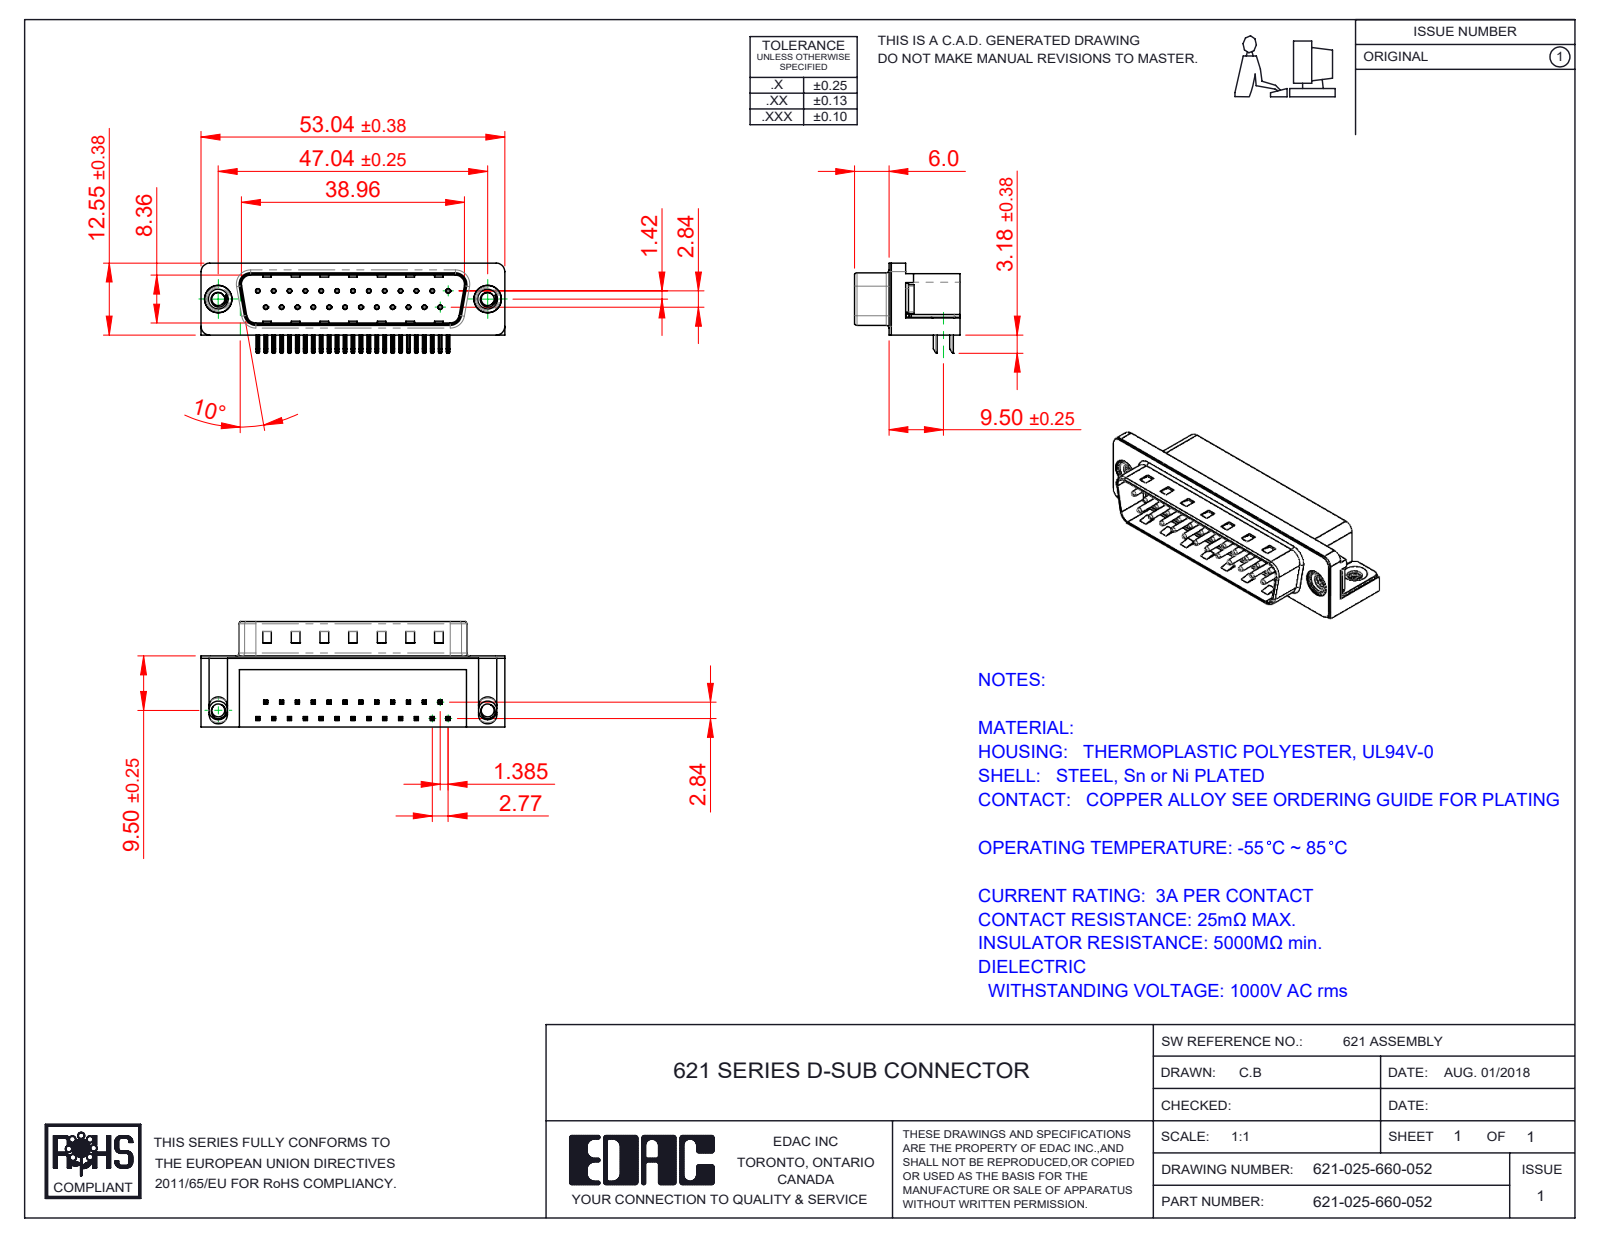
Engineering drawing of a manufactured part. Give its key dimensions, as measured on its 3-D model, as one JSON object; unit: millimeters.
{"part_name": "621 Contact Top; 621-025-660-052; 621 Shell_25 Socket; 621 4-40 Threaded Board Mount (+3 more)", "step_written_by": "SolidWorks 2016 (CONFIG_CONTROL_DESIGN)", "units": "millimeters", "bodies": {"solids": 31, "faces": 2293, "planar": 1405, "cylindrical": 671, "other": 217}, "overall_size": [53.04, 18.4, 15.73], "volume_mm3": 6360, "surface_area_mm2": 7762, "round_holes": [[0.35, 25], [0.8, 25], [2.26, 4], [4, 2], [4.8, 2], [5, 2]], "round_bosses_or_shafts": [[0.75, 25], [4.9, 2], [4.75, 2], [3.9, 2], [3.26, 2]], "partial_cylinders_radius": [[0.25, 108], [0.12, 50], [1, 16], [0.5, 9], [1.6, 8], [1.5, 7], [0.9, 4], [2, 4]], "face_to_face_distances": [0.4, 12, 10.35, 2.1, 8.76, 10.46, 1.7, 10.86, 12.4, 9], "hole_center_spacings": [3.16, 2.77, 5.54, 8.31, 11.08, 13.85, 16.62, 5.03]}
